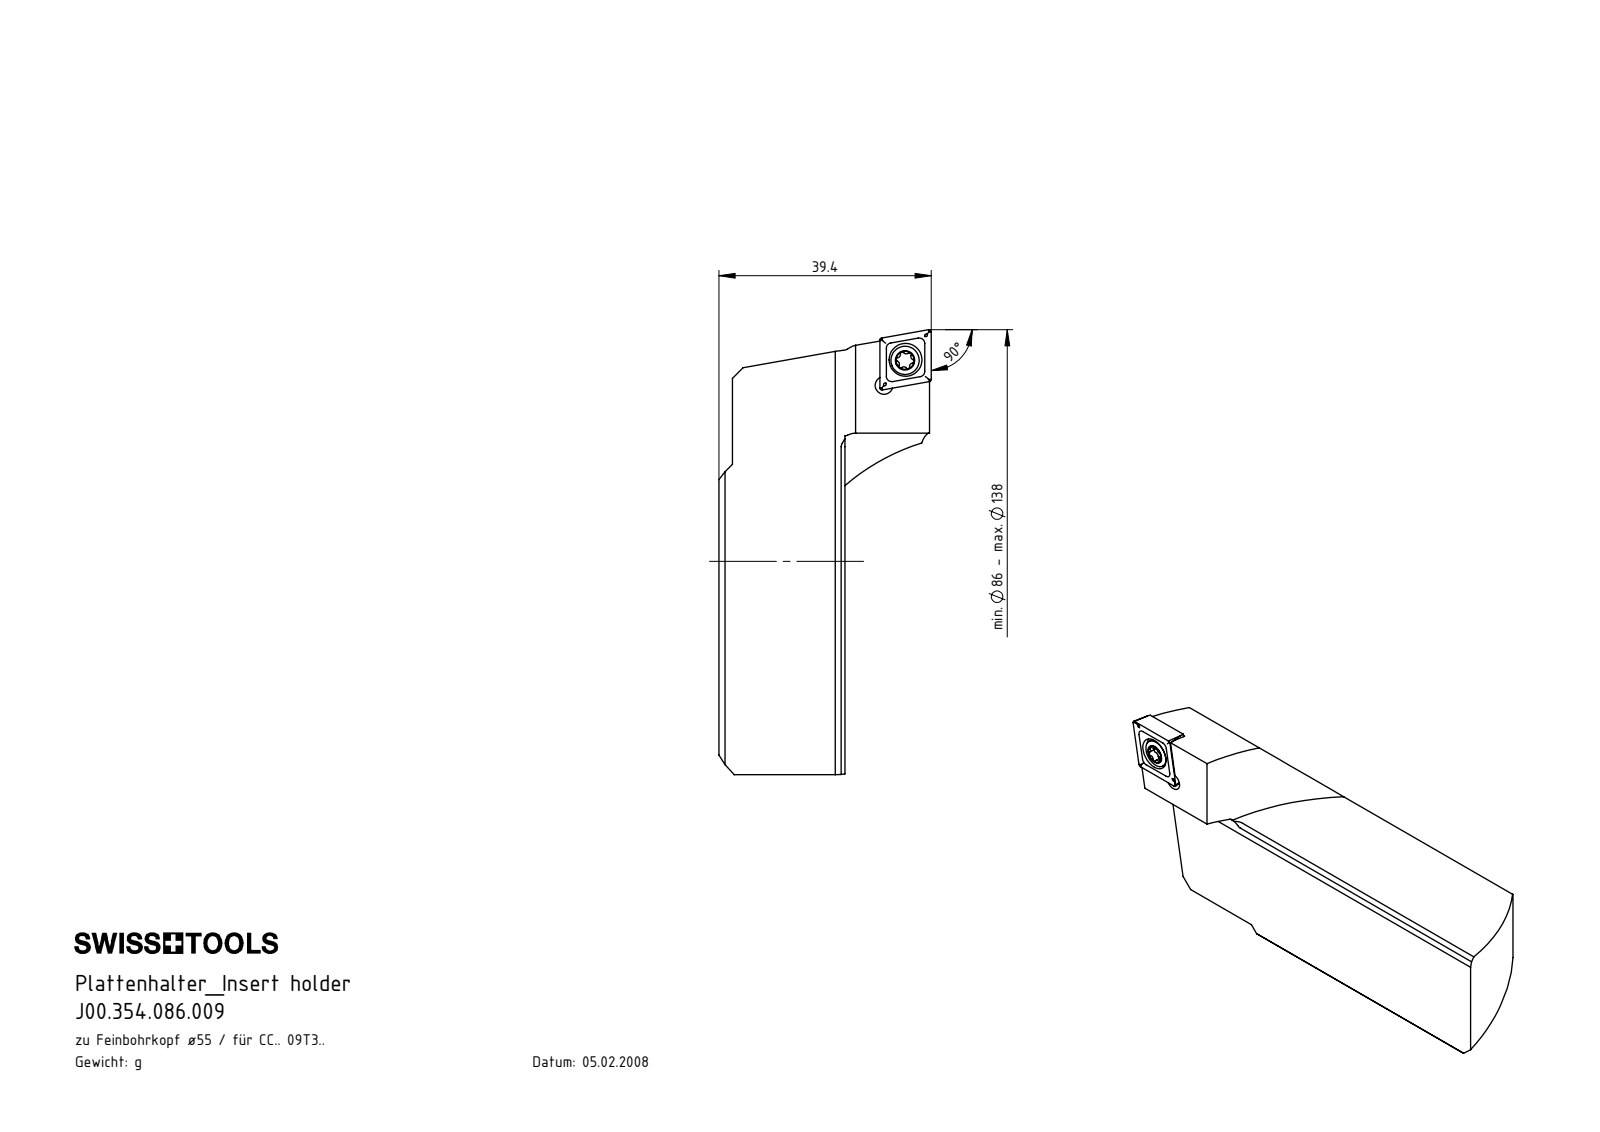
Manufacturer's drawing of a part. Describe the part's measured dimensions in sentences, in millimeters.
The part is named "J00.354.086.009; WCB-ER2.001.009_A; CCMT09T304; F00-WCB.086.001_C". Its 3-D file was written by "SolidWorks 2017 (CONFIG_CONTROL_DESIGN)". It is 3 solids with 382 faces: 226 planar, 39 cylindrical and 117 other. Overall it measures 82.57 by 39.4 by 27.35 millimeters. Its volume is 33 561 cubic millimeters and its surface area 8 976 square millimeters. Round holes: 2 of diameter 3.3, 1 of diameter 4.4, 1 of diameter 6.1. Round bosses or shafts: 1 of diameter 5.25, 1 of diameter 4. Partial cylindrical surfaces (rounded edges, fillets, slot ends): 8 of radius 0.2, 6 of radius 0.34, 6 of radius 0.59, 3 of radius 40, 1 of radius 0.8. The main face-to-face distances are 2.38, 4.76, 21.3, 7.14, 9.52, 4.77, 7.15, 9.53, 11.91, 11.9. The hole center spacings are 6.07, 6.19.
